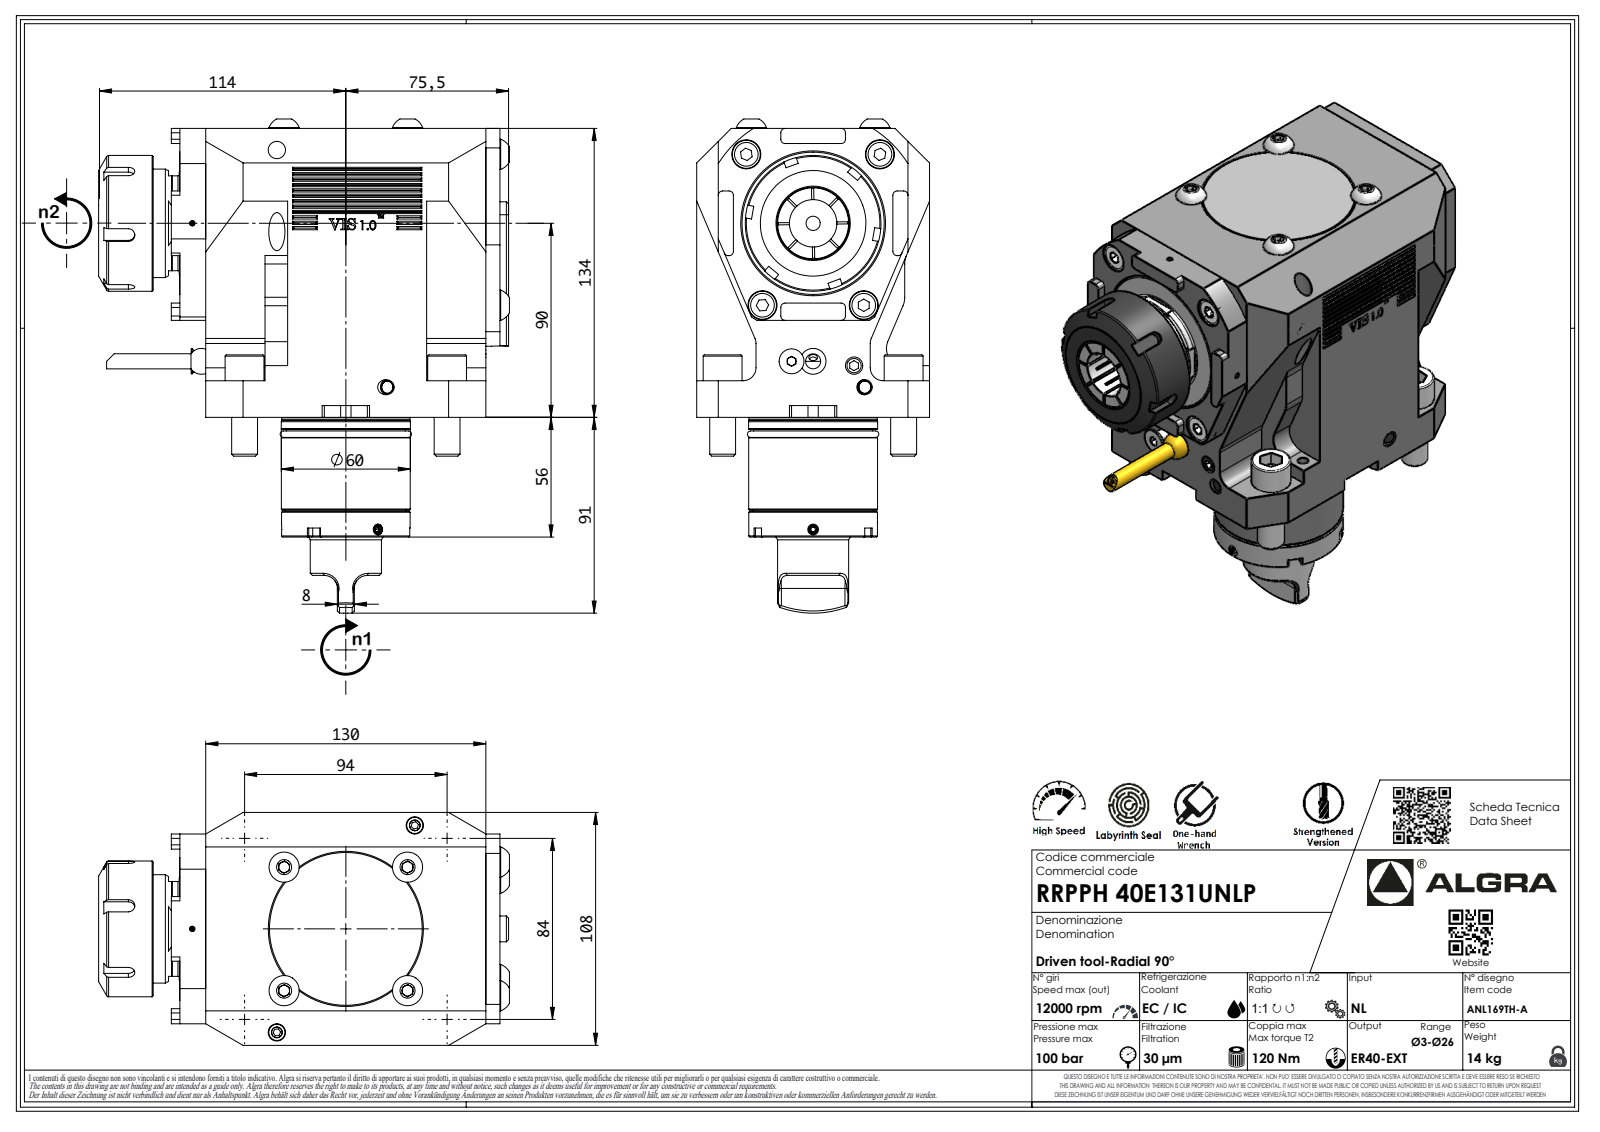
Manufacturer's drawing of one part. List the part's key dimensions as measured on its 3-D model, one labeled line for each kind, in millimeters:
Part name (STEP PRODUCT): RRPPH40E131UNLP
STEP written by: SolidWorks 2023 (AUTOMOTIVE_DESIGN)
Units: millimetres
Bodies: 1 solid, 1021 faces (688 planar, 140 cylindrical, 193 other)
Overall size (bounding box): 224.8 × 190.2 × 108
Volume: 2 081 000 mm³ · Surface area: 132 832 mm²
Round holes (diameter × count): ⌀2.1 ×1, ⌀4 ×1
Round bosses / shafts (diameter × count): ⌀18 ×4, ⌀12 ×4, ⌀63 ×1, ⌀59.9 ×1, ⌀59.8 ×1, ⌀59.7 ×1, ⌀59.5 ×1, ⌀55.2 ×1
Partial cylindrical surfaces — rounded edges, fillets, slot ends (radius × count): R0.2 ×21, R8 ×18, R2 ×16, R6 ×11, R3 ×9, R0.33 ×7, R0.52 ×7, R3.7 ×7
Main face-to-face distances: 108, 134, 27.5, 12, 102.5, 6.5, 136.5, 38, 5.5, 148.5
